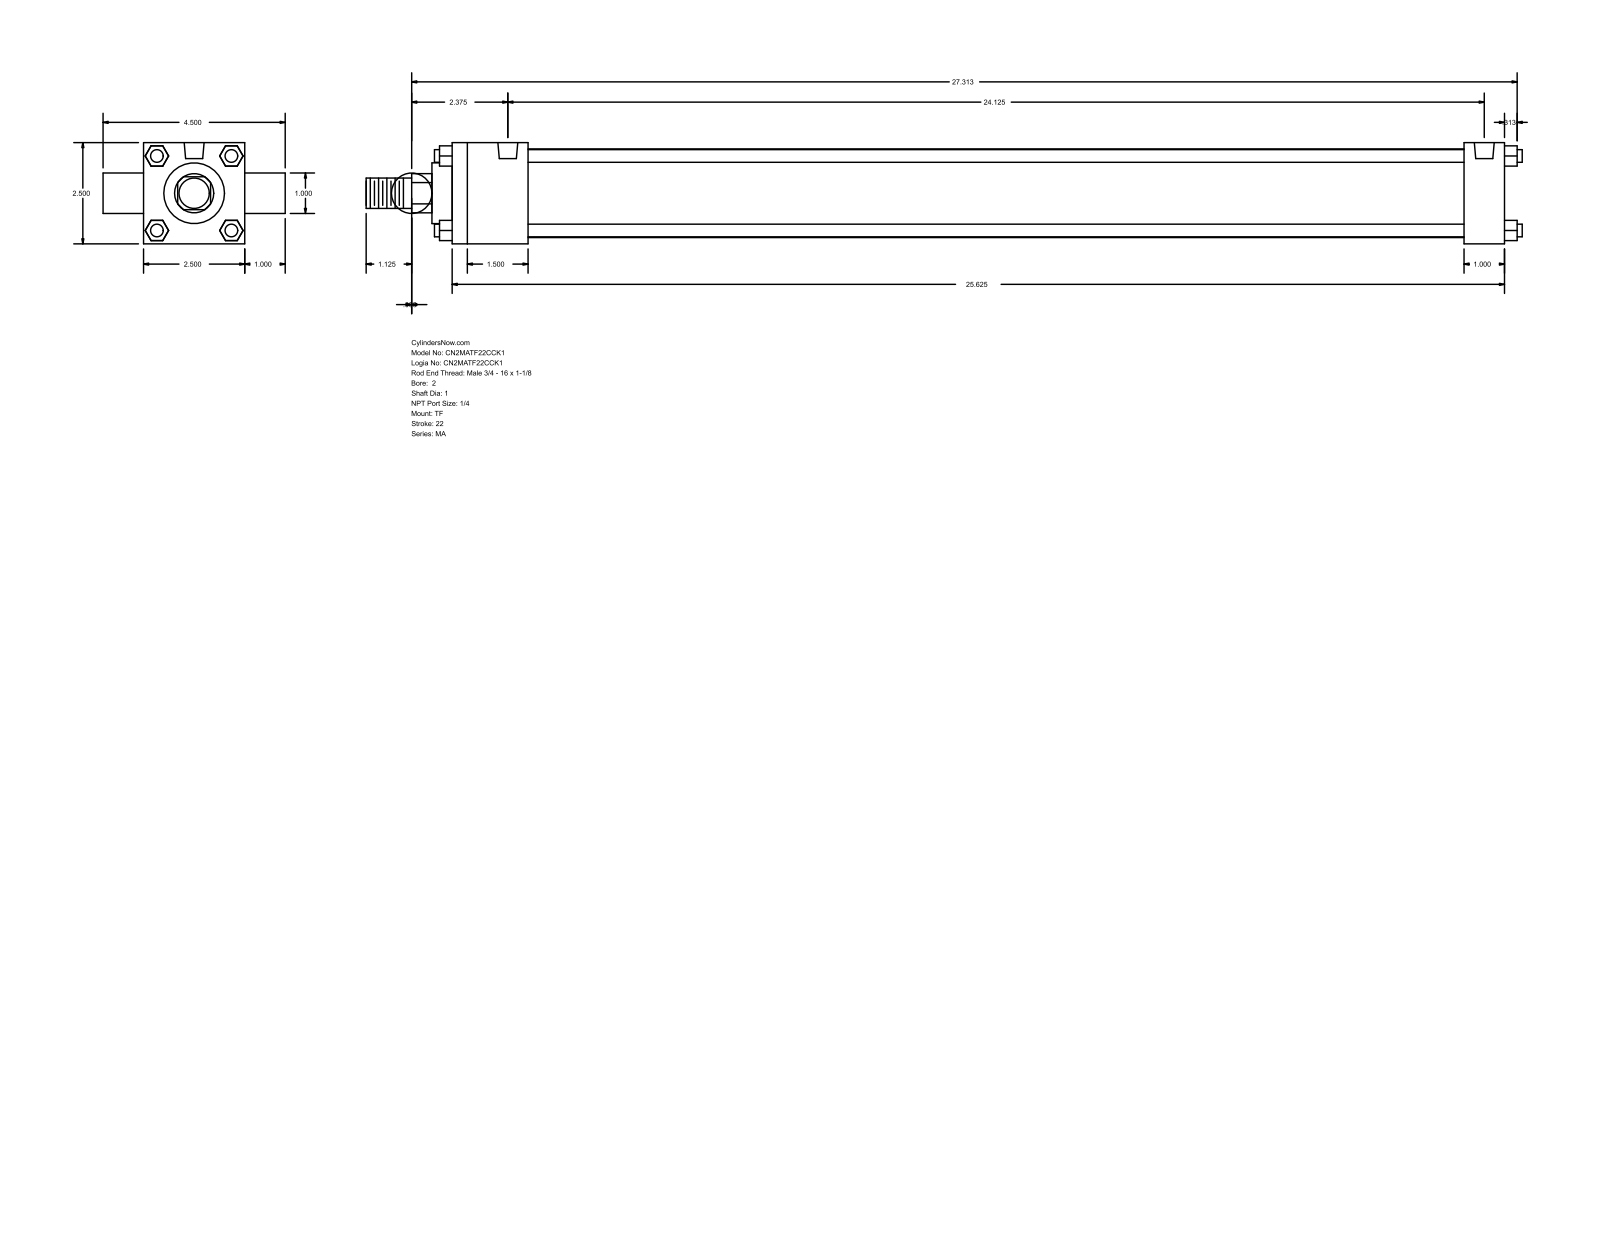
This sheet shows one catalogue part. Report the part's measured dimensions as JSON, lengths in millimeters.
{"part_name": "MA_TF__0200_1", "step_written_by": "GSSL Pune (CONFIG_CONTROL_DESIGN)", "units": "millimeters", "bodies": {"solids": 0, "faces": 120, "planar": 92, "cylindrical": 28, "other": 0}, "overall_size": [725.49, 114.3, 63.5], "round_holes": [[7.94, 3], [12.49, 2]], "round_bosses_or_shafts": [[7.94, 4], [25.4, 2], [55.63, 1], [38.1, 1], [19.05, 1]], "partial_cylinders_radius": [[12.29, 1]], "face_to_face_distances": [63.5, 25.4, 660.4, 12.7, 47.63, 635, 587.37, 612.77, 88.9, 40.47], "hole_center_spacings": [612.77]}
